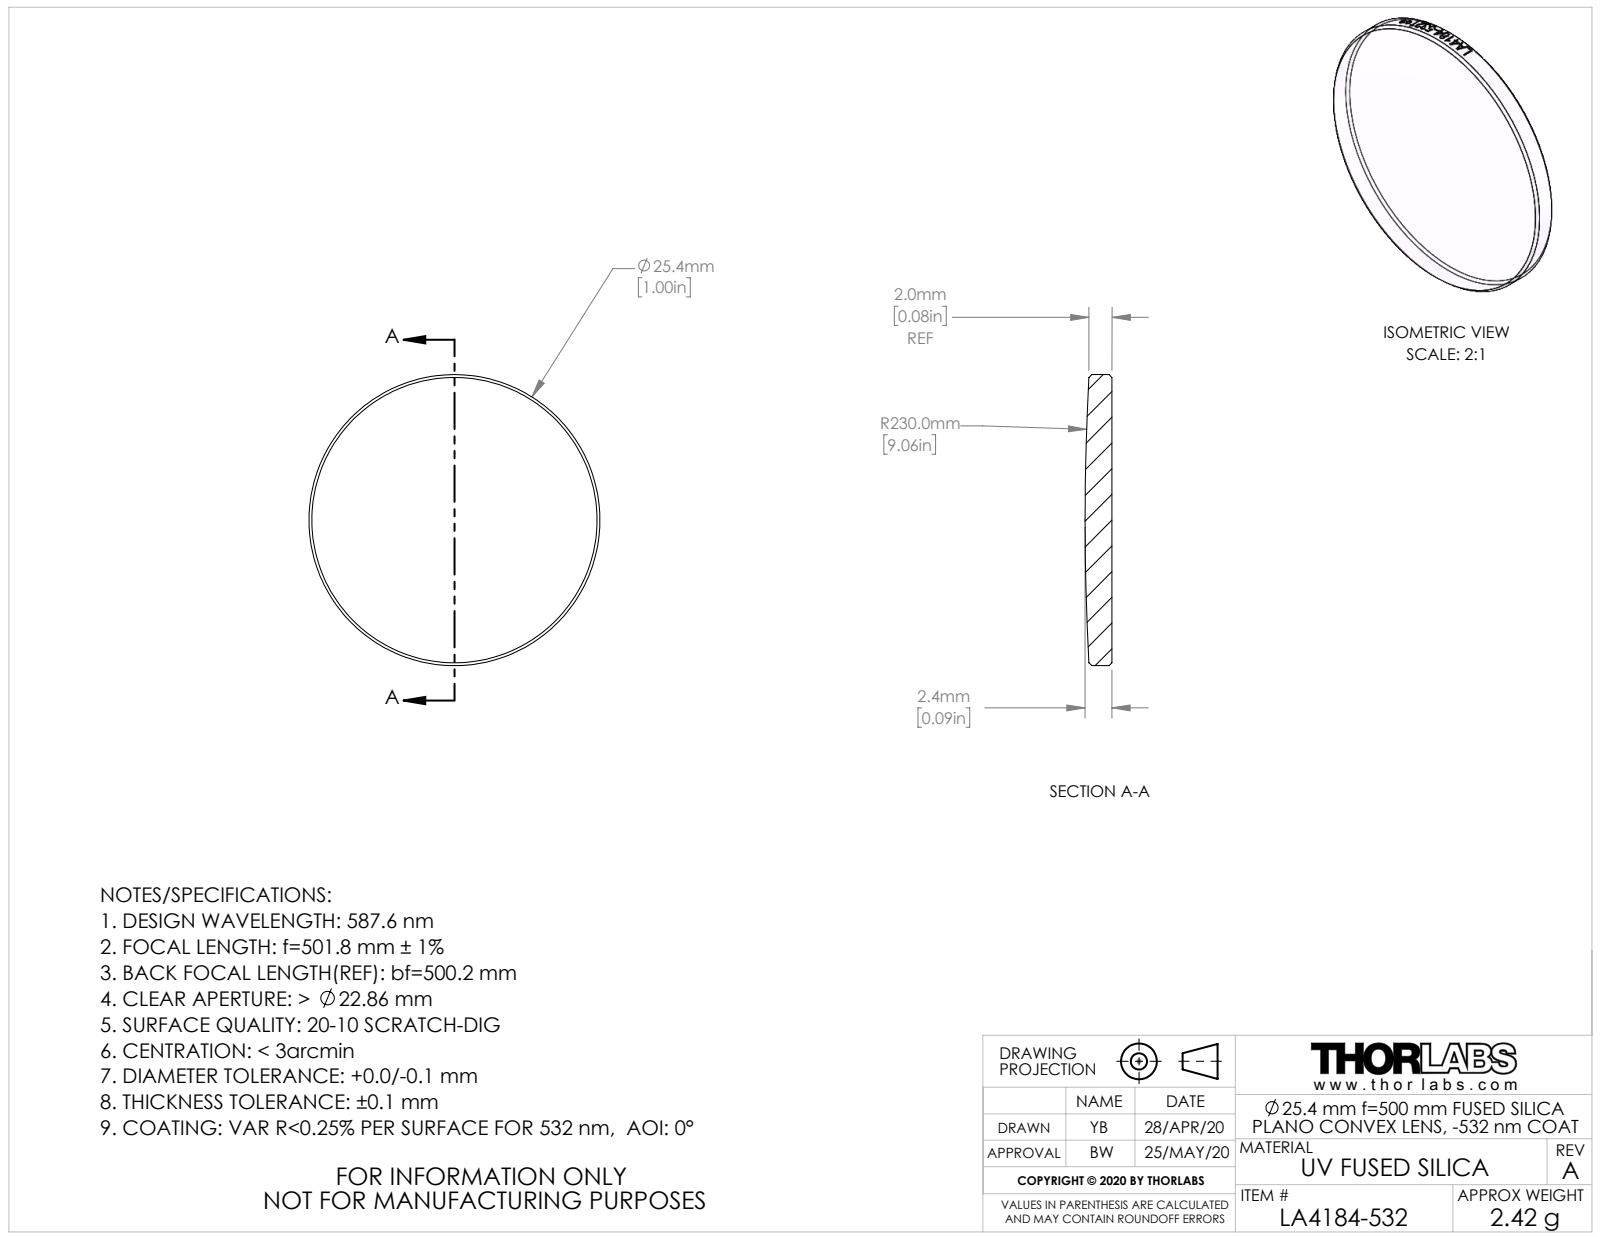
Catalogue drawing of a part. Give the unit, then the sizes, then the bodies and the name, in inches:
Units: inches
Overall size (bounding box): 1 × 1 × 0.093
Round bosses / shafts (diameter × count): ⌀1 ×1
Volume: 0.067 in³ · Surface area: 1.784 in²
Bodies: 1 solid, 32 faces (1 planar, 25 cylindrical, 6 other)
Part name (STEP PRODUCT): CTN015732-E0W
STEP written by: SolidWorks 2018 (AUTOMOTIVE_DESIGN)
